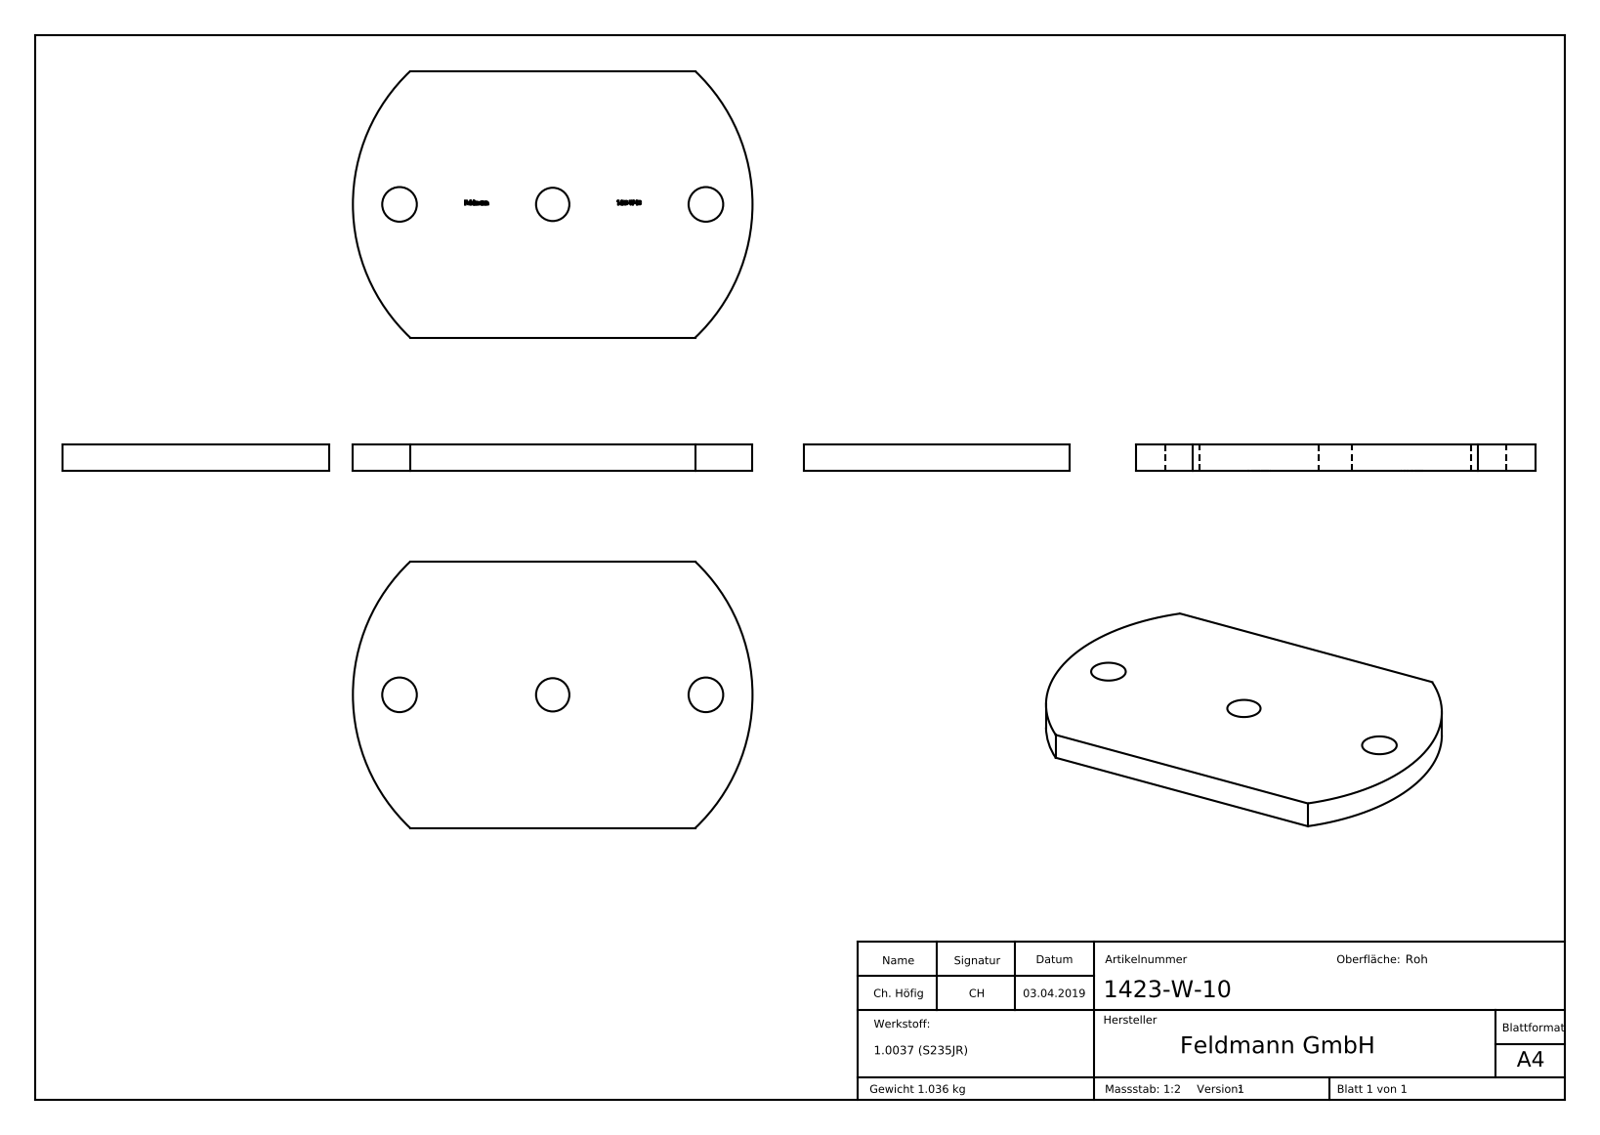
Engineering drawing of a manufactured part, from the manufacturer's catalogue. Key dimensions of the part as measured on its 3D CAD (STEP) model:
Part name (STEP PRODUCT): 1423-W-10
STEP written by: SolidWorks 2015 (CONFIG_CONTROL_DESIGN)
Units: millimetres
Bodies: 1 solid, 220 faces (135 planar, 8 cylindrical, 77 other)
Overall size (bounding box): 150 × 100 × 10
Volume: 132 818 mm³ · Surface area: 32 160 mm²
Round holes (diameter × count): ⌀13 ×2, ⌀12.5 ×1
Partial cylindrical surfaces — rounded edges, fillets, slot ends (radius × count): R68.89 ×2
Main face-to-face distances: 10, 100, 9.9, 0.54, 55.47, 62.53, 7.06, 1.12, 2.03, 57.5
Hole centre spacings: 57.5, 115
